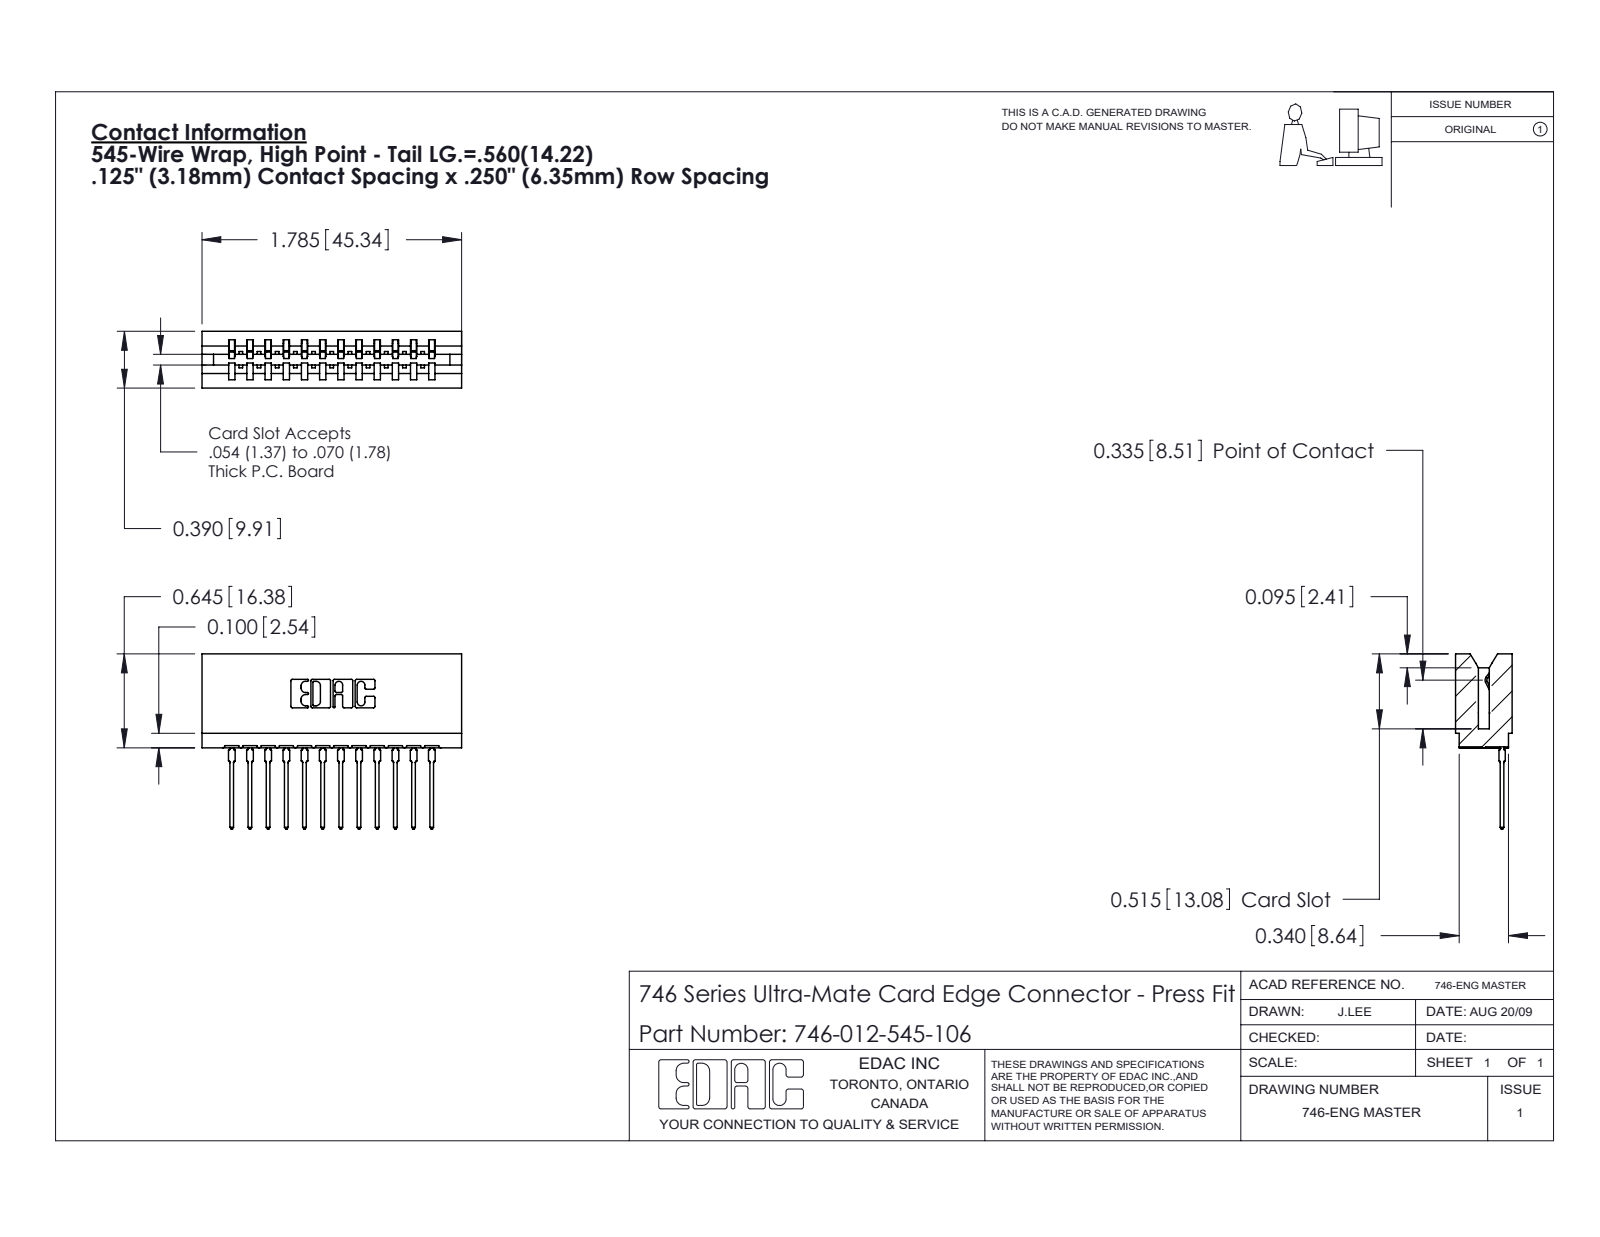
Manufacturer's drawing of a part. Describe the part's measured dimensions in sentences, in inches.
The part is named "746 Part_.515 Slot Depth - 06; 746-012-545-106; 746-292-001_545". Its 3-D file was written by "SolidWorks 2020 (CONFIG_CONTROL_DESIGN)". It is 13 solids with 1394 faces: 812 planar, 270 cylindrical and 312 other. Overall it measures 1.785 by 1.204 by 0.39 inches. Its volume is 0.302 cubic inches and its surface area 10.88 square inches. Partial cylindrical surfaces (rounded edges, fillets, slot ends): 24 of radius 0.021, 22 of radius 0.01, 13 of radius 0.015, 6 of radius 0.007, 6 of radius 0.031, 4 of radius 0.005, 4 of radius 0.011, 3 of radius 0.026. The main face-to-face distances are 0.25, 0.333, 0.5, 0.057, 0.125, 0.125, 0.39, 0.042, 0.208, 0.458.
